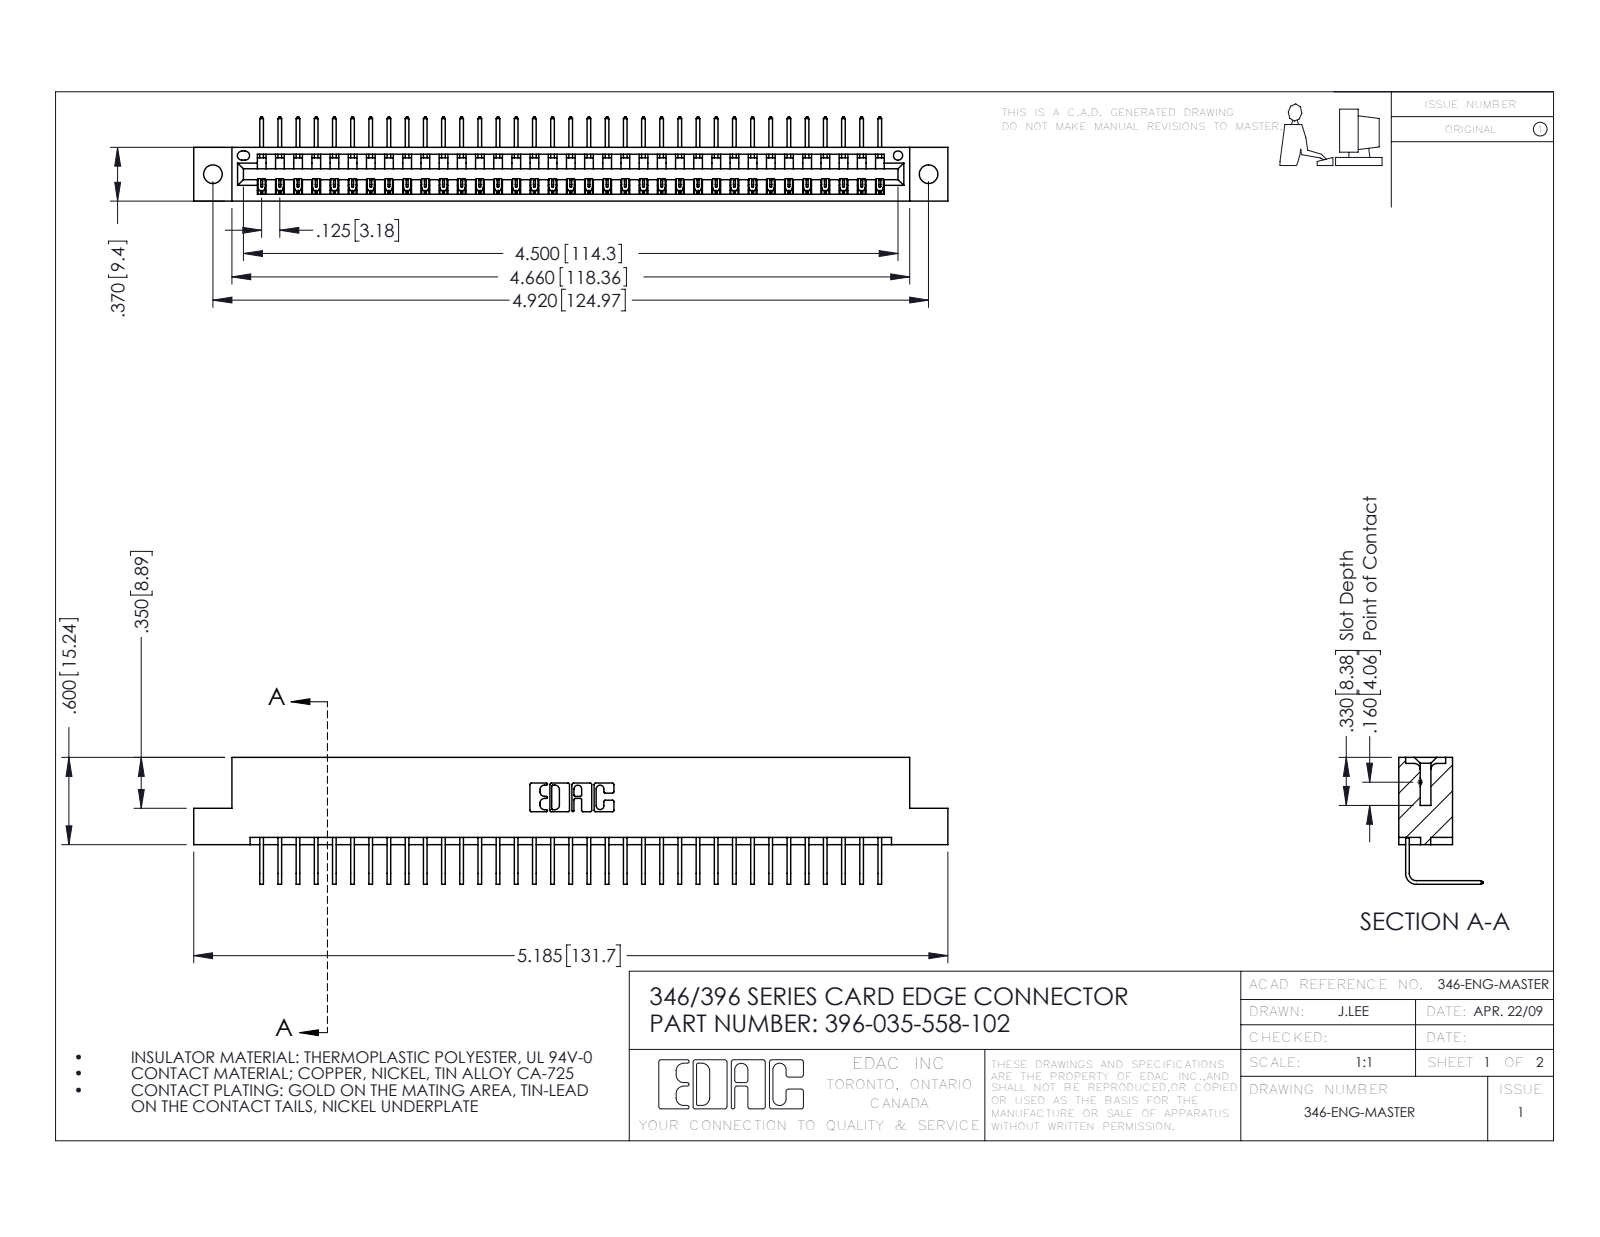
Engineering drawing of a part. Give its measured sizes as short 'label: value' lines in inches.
name: 345-292-001_558 Tail - 2; 346 Part_Flush Mounting Lugs - 0.128 Dia; 396-035-558-102
written by: SolidWorks 2016 (CONFIG_CONTROL_DESIGN)
unit: in
bodies: 36 solids, 2222 faces (1546 planar, 676 cylindrical, 0 other)
size: 5.185 × 0.873 × 0.58
volume: 0.771 in³; area: 25.02 in²
holes: 2× ⌀0.128, 1× ⌀0.064
rounds: 70× R0.006, 22× R0.01, 6× R0.007, 6× R0.031, 3× R0.026, 2× R0.031, 2× R0.04, 1× R0.014
face distances: 0.322, 0.048, 0.37, 0.25, 0.298, 0.025, 0.072, 0.148, 0.222, 0.1
hole spacings: 0.246, 4.711, 4.92
